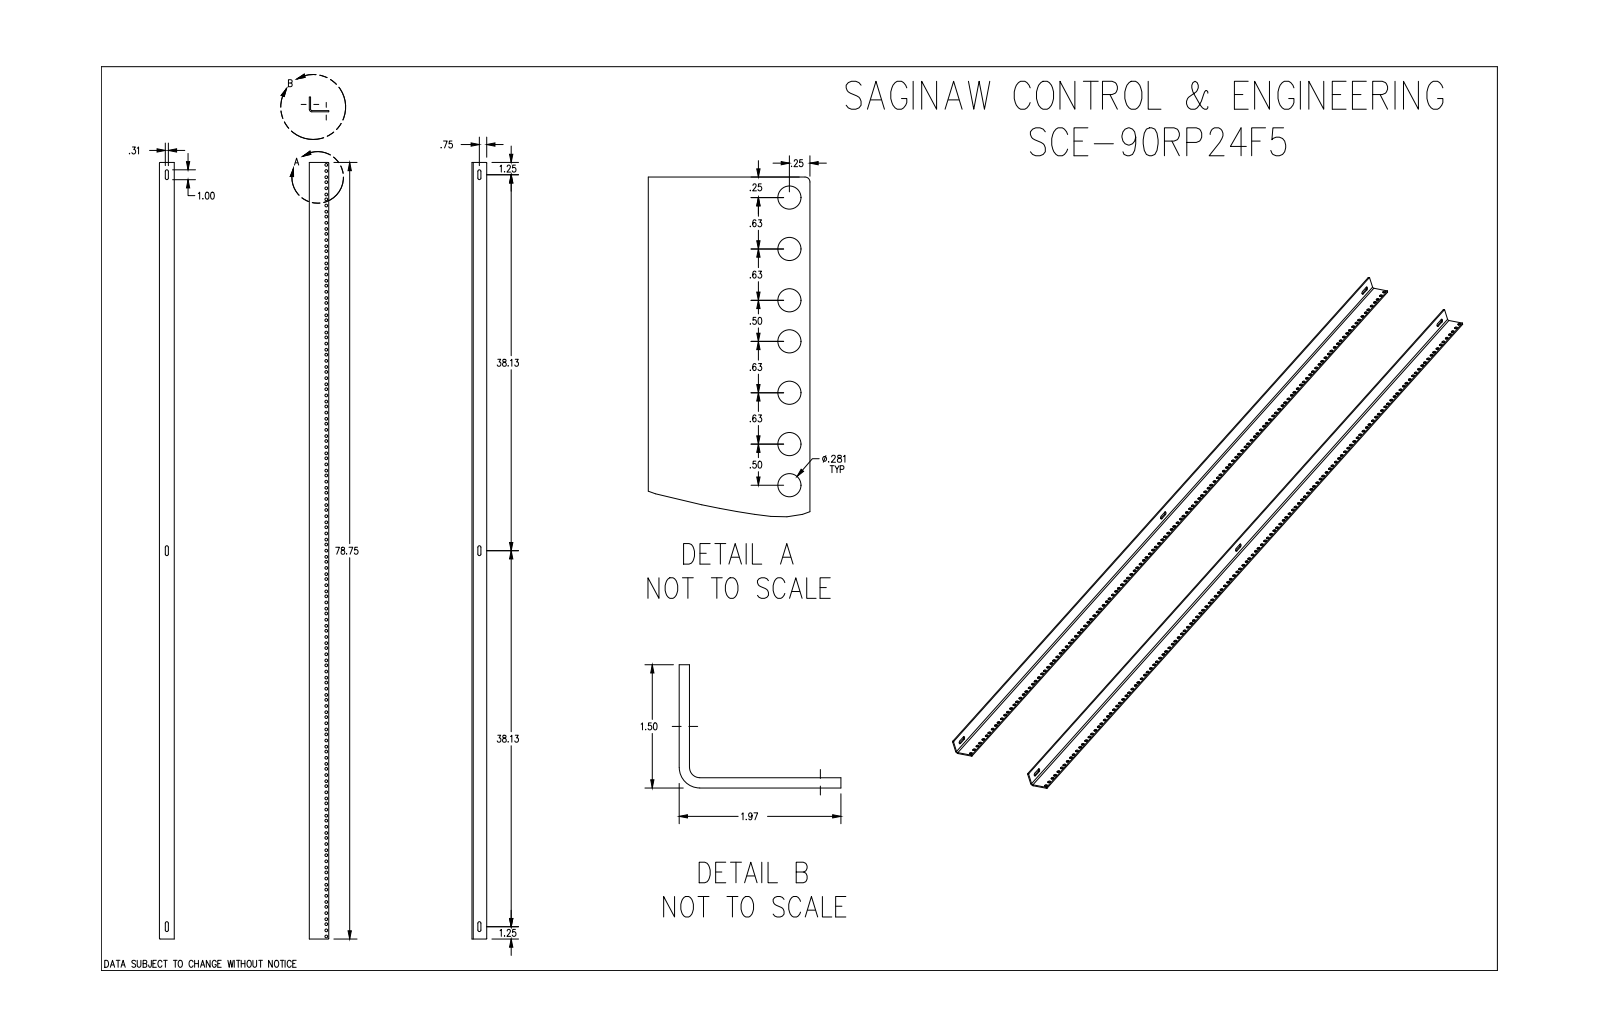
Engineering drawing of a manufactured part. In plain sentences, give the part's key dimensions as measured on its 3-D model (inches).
The part is named "SCE-90RP24F5". Its 3-D file was written by "SolidWorks 2019 (AUTOMOTIVE_DESIGN)". It is 1 solid with 300 faces: 18 planar, 282 cylindrical and 0 other. Overall it measures 78.75 by 1.969 by 1.5 inches. Its volume is 30.97 cubic inches and its surface area 531.7 square inches. Round holes: 135 of diameter 0.281. Partial cylindrical surfaces (rounded edges, fillets, slot ends): 6 of radius 0.156, 4 of radius 0.06, 1 of radius 0.125, 1 of radius 0.25. The main face-to-face distances are 0.125, 1.375, 1.5, 1.969, 1.844, 0.594, 0.906, 78.75, 0.313, 0.781. The hole center spacings are 1.75, 3.5, 5.25, 7, 8.75, 0.625, 0.625, 1.25.
